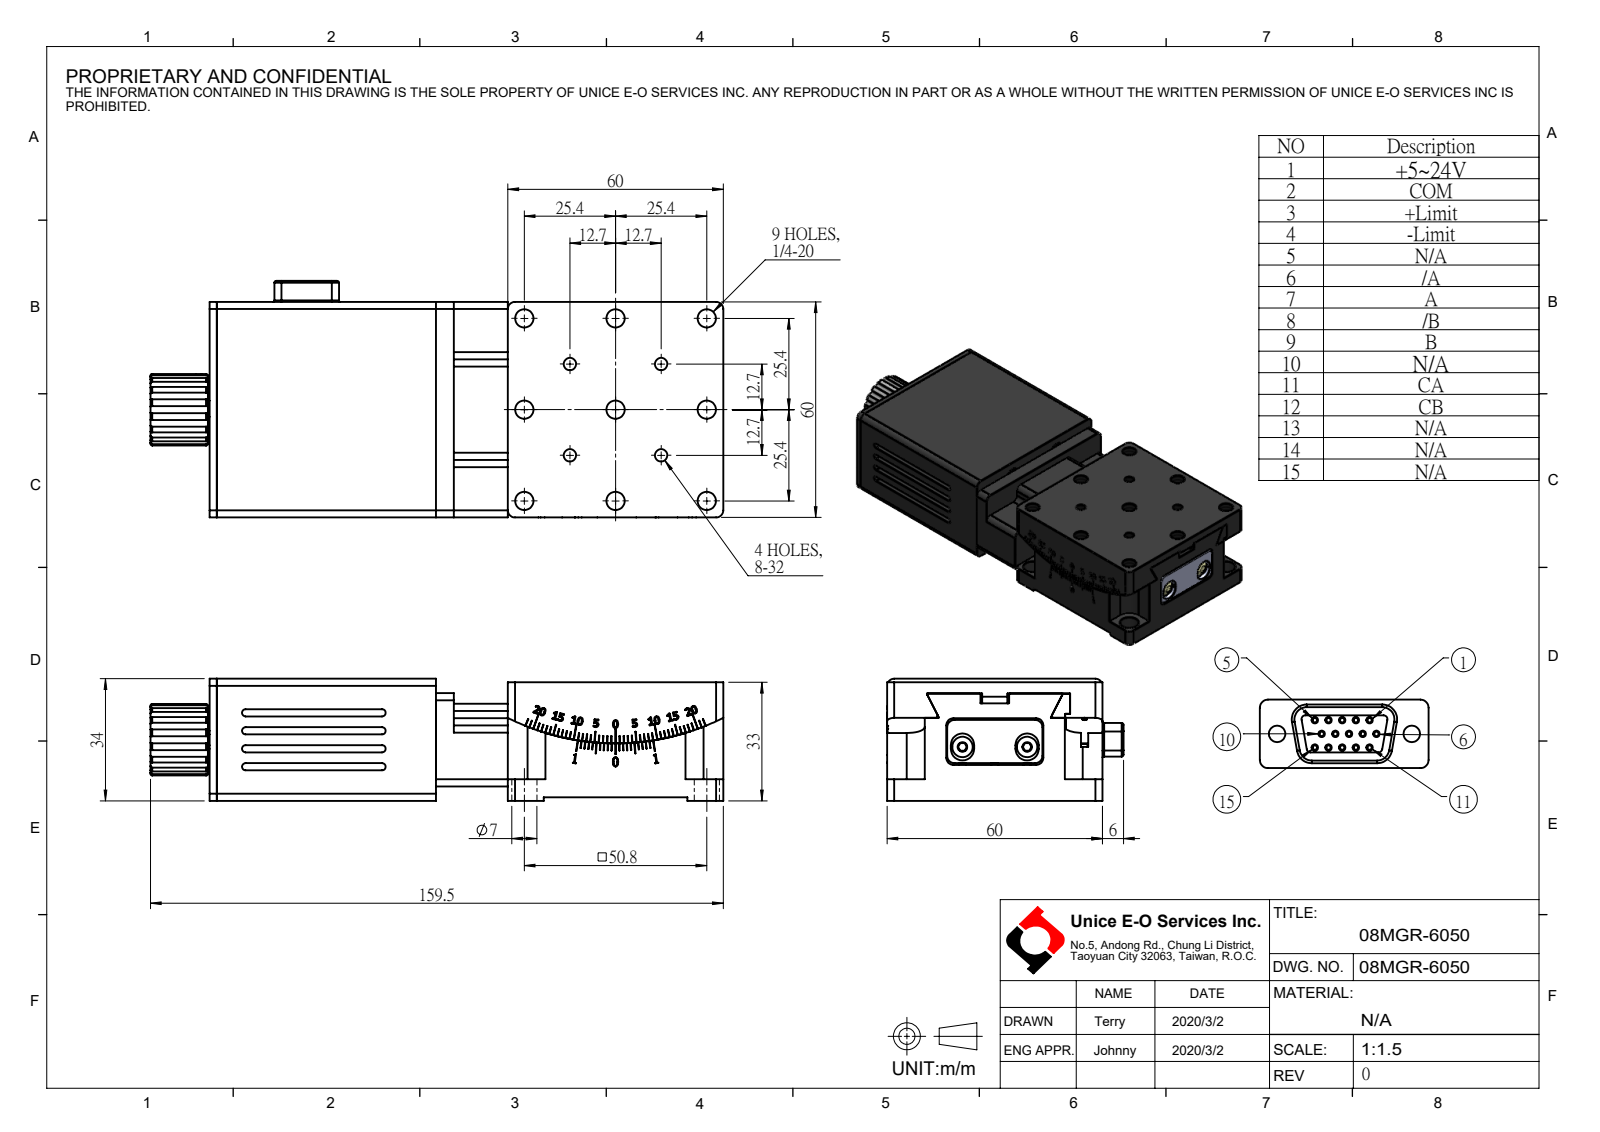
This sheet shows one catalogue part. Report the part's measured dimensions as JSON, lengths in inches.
{"part_name": "08MGR-6050", "step_written_by": "SolidWorks 2016 (CONFIG_CONTROL_DESIGN)", "units": "inches", "bodies": {"solids": 0, "faces": 731, "planar": 331, "cylindrical": 254, "other": 146}, "overall_size": [6.28, 2.592, 1.339], "round_holes": [[0.031, 15], [0.063, 10], [0.201, 9], [0.094, 4], [0.136, 4], [0.217, 4], [0.276, 4], [0.098, 3], [0.089, 2], [0.12, 2], [0.906, 1]], "round_bosses_or_shafts": [[0.63, 1], [0.362, 1], [0.054, 1]], "partial_cylinders_radius": [[0.079, 30], [0.039, 24], [0.02, 8], [0.059, 8], [0.128, 4], [0.197, 4], [0.069, 2], [0.394, 1]], "face_to_face_distances": [1.299, 0.039, 2.362, 1.339, 1.26, 0.787, 3.268, 0.118, 0.197, 0.413], "hole_center_spacings": [0.112, 0.707, 1, 1.581, 0.18, 0.2, 0.1, 0.269]}
